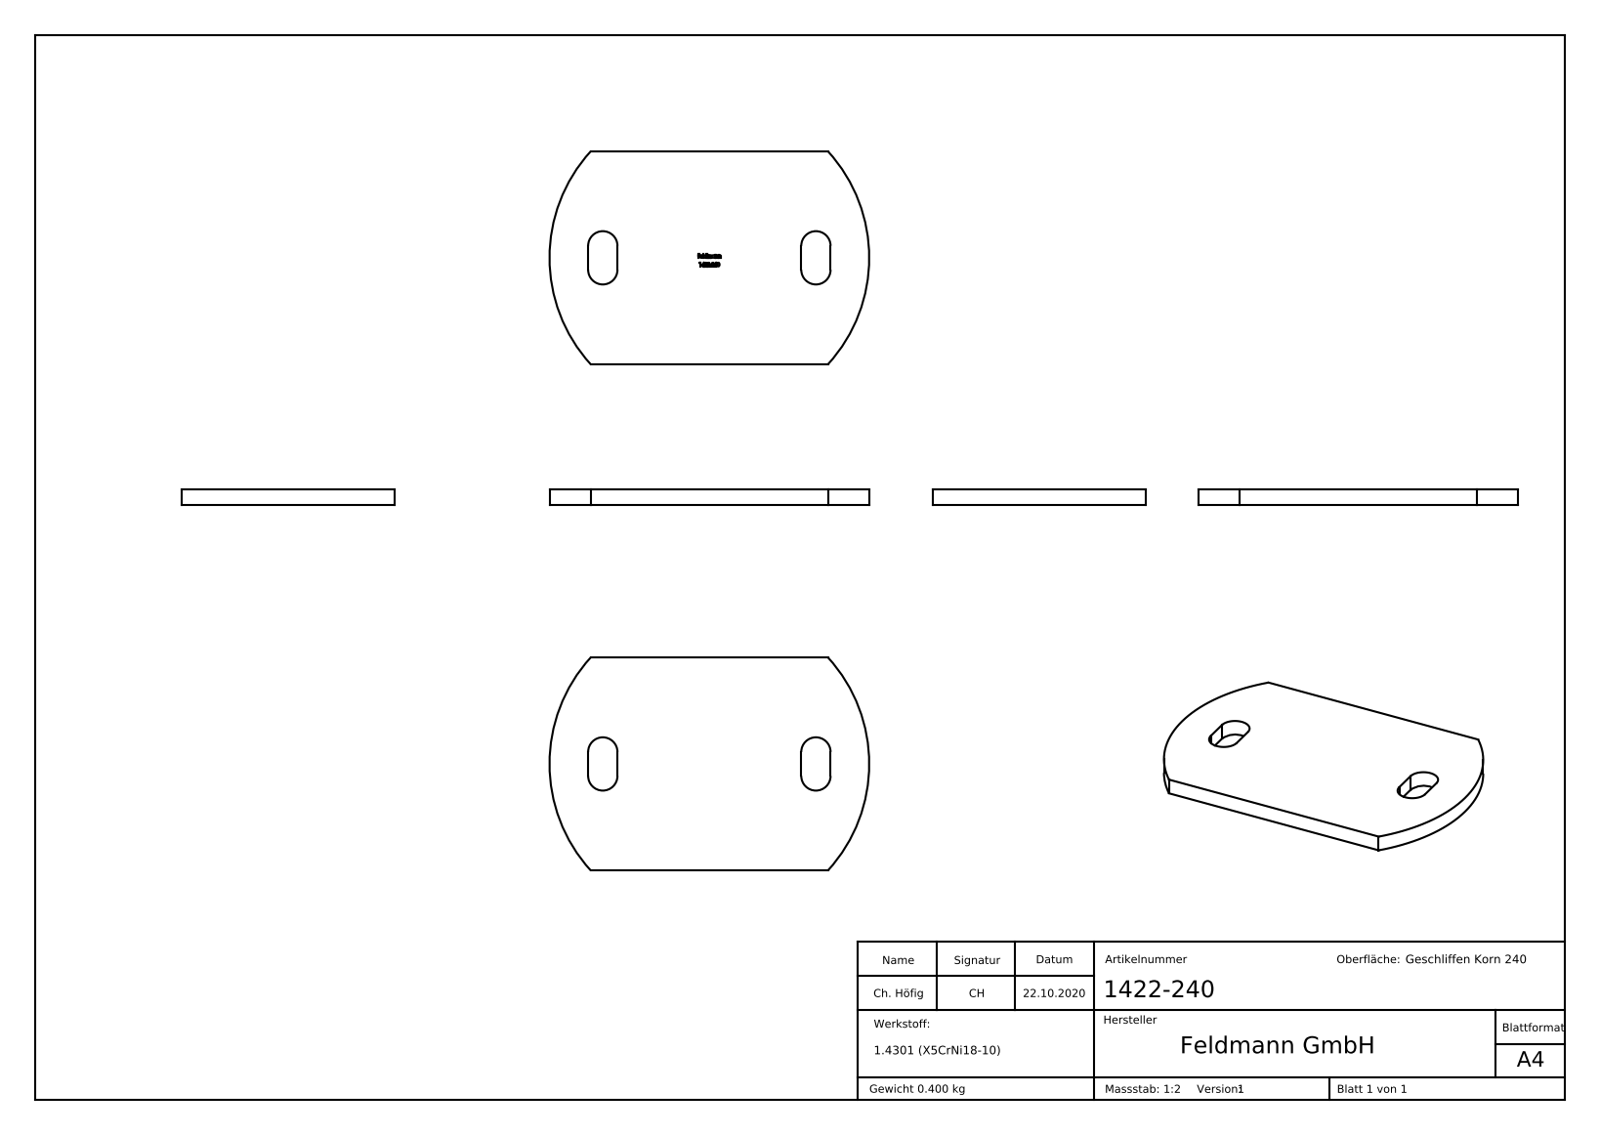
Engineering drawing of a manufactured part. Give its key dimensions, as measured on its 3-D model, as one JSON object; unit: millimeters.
{"part_name": "1422-240", "step_written_by": "SolidWorks 2018 (CONFIG_CONTROL_DESIGN)", "units": "millimeters", "bodies": {"solids": 1, "faces": 221, "planar": 138, "cylindrical": 8, "other": 75}, "overall_size": [120, 80, 6], "volume_mm3": 50603, "surface_area_mm2": 19629, "partial_cylinders_radius": [[5.5, 4], [59.36, 2]], "face_to_face_distances": [6, 80, 11, 91, 69, 5.9, 36.81, 43.19, 40, 1.26]}
